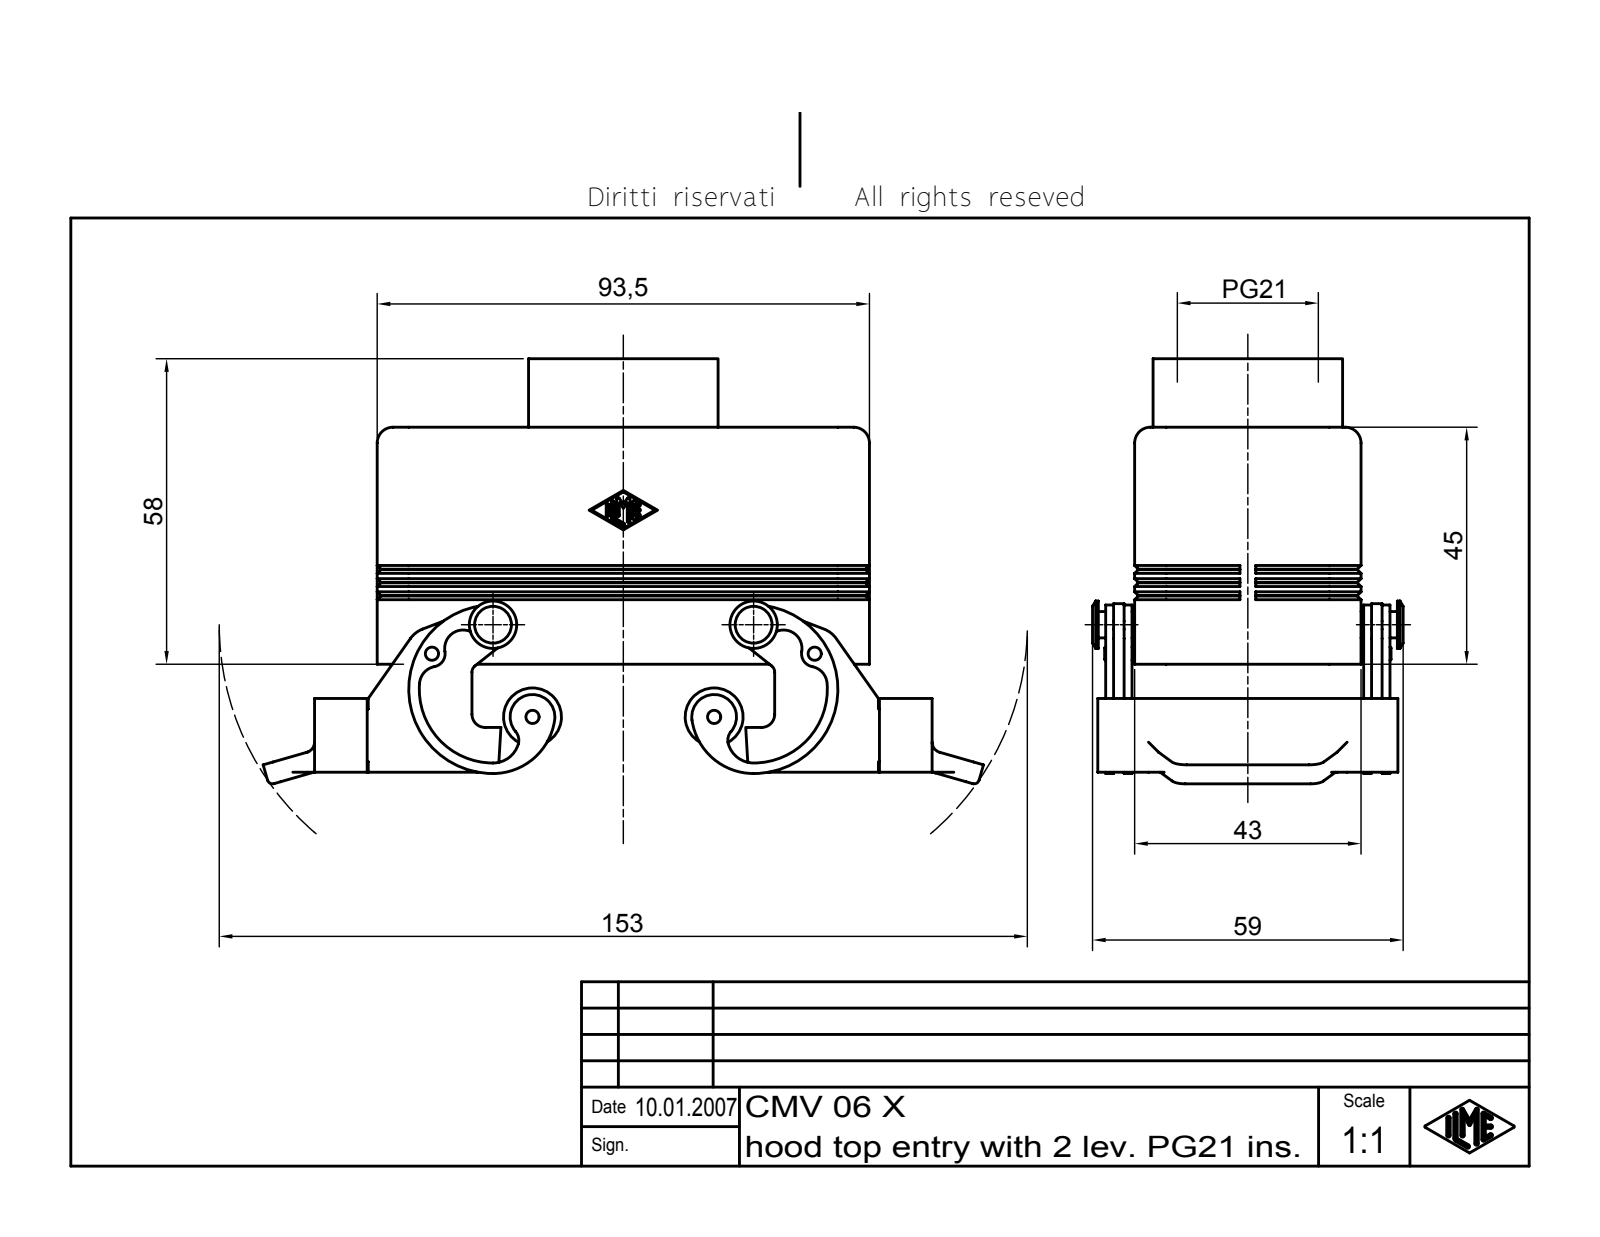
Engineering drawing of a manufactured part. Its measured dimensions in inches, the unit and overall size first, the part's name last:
Units: inches
Overall size (bounding box): 5.387 × 3.178 × 2.323
Round holes (diameter × count): ⌀0.098 ×2, ⌀0.851 ×1, ⌀1.054 ×1
Round bosses / shafts (diameter × count): ⌀0.433 ×2, ⌀0.354 ×2, ⌀0.197 ×2, ⌀0.079 ×2, ⌀1.417 ×1
Partial cylindrical surfaces — rounded edges, fillets, slot ends (radius × count): R0.01 ×14, R0.118 ×12, R0.079 ×10, R0.039 ×6, R0.098 ×6, R0.138 ×4, R0.197 ×4, R0.236 ×4
Main face-to-face distances: 0.118, 1.575, 1.457, 1.693, 0.335, 0.079, 0.453, 1.85, 1.772, 1.654
Hole centre spacings: 2.862
Volume: 4.735 in³ · Surface area: 76.08 in²
Bodies: 1 solid, 738 faces (215 planar, 191 cylindrical, 332 other)
Part name (STEP PRODUCT): CHV Tüllengehäuse 2 Bügel für einen Einsatz
STEP written by: Autodesk Inventor 7 (AUTOMOTIVE_DESIGN)
